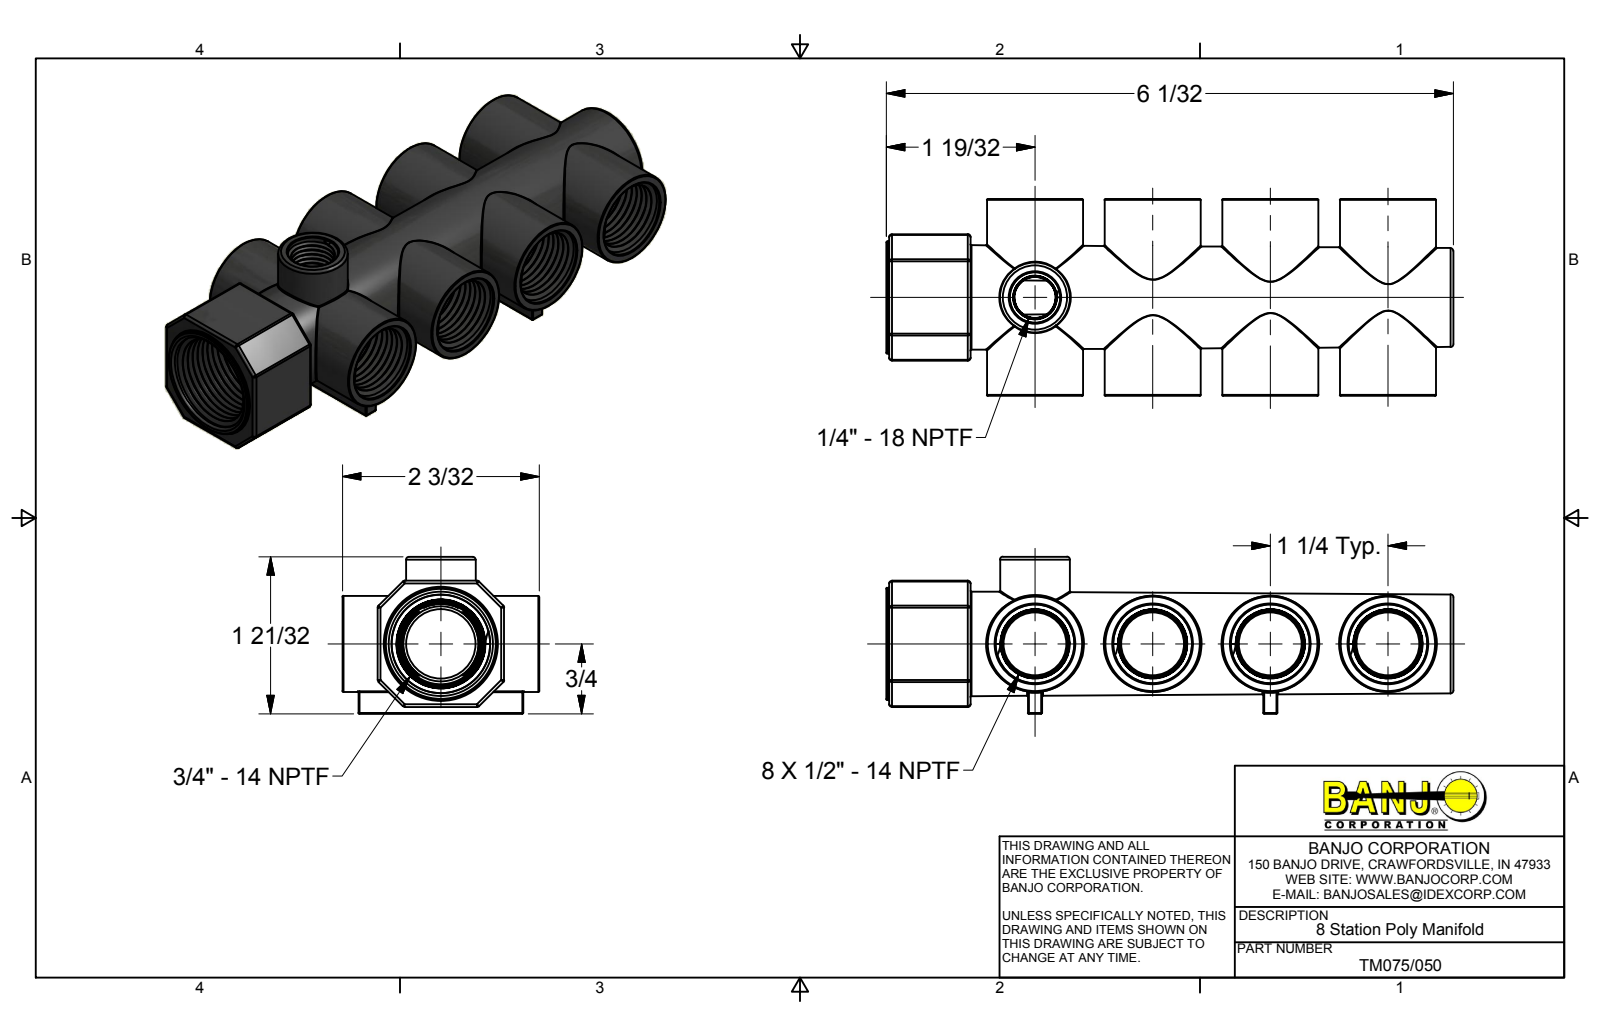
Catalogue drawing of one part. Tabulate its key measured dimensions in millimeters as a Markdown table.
| quantity | value |
| --- | --- |
| part name | TM075_050 |
| STEP written by | Autodesk Inventor 2014 (AUTOMOTIVE_DESIGN) |
| units | millimeters |
| bodies | 0 solids, 359 faces (43 planar, 76 cylindrical, 240 other) |
| overall size | 153.03 × 53.11 × 42.35 |
| round holes (diameter × count) | 17.02 × 4 |
| round bosses / shafts (diameter × count) | 25.91 × 4, 30.23 × 1, 18.8 × 1 |
| partial cylindrical surfaces (radius × count) | 0.76 × 24, 0.25 × 18, 6.6 × 4, 4.34 × 1, 7.92 × 1 |
| main face-to-face distances | 9.52, 43.6, 34.08, 53.12, 3.81, 63.5, 14.61, 38.51, 5.09, 28.99 |
| hole center spacings | 31.75, 63.5, 95.25 |
